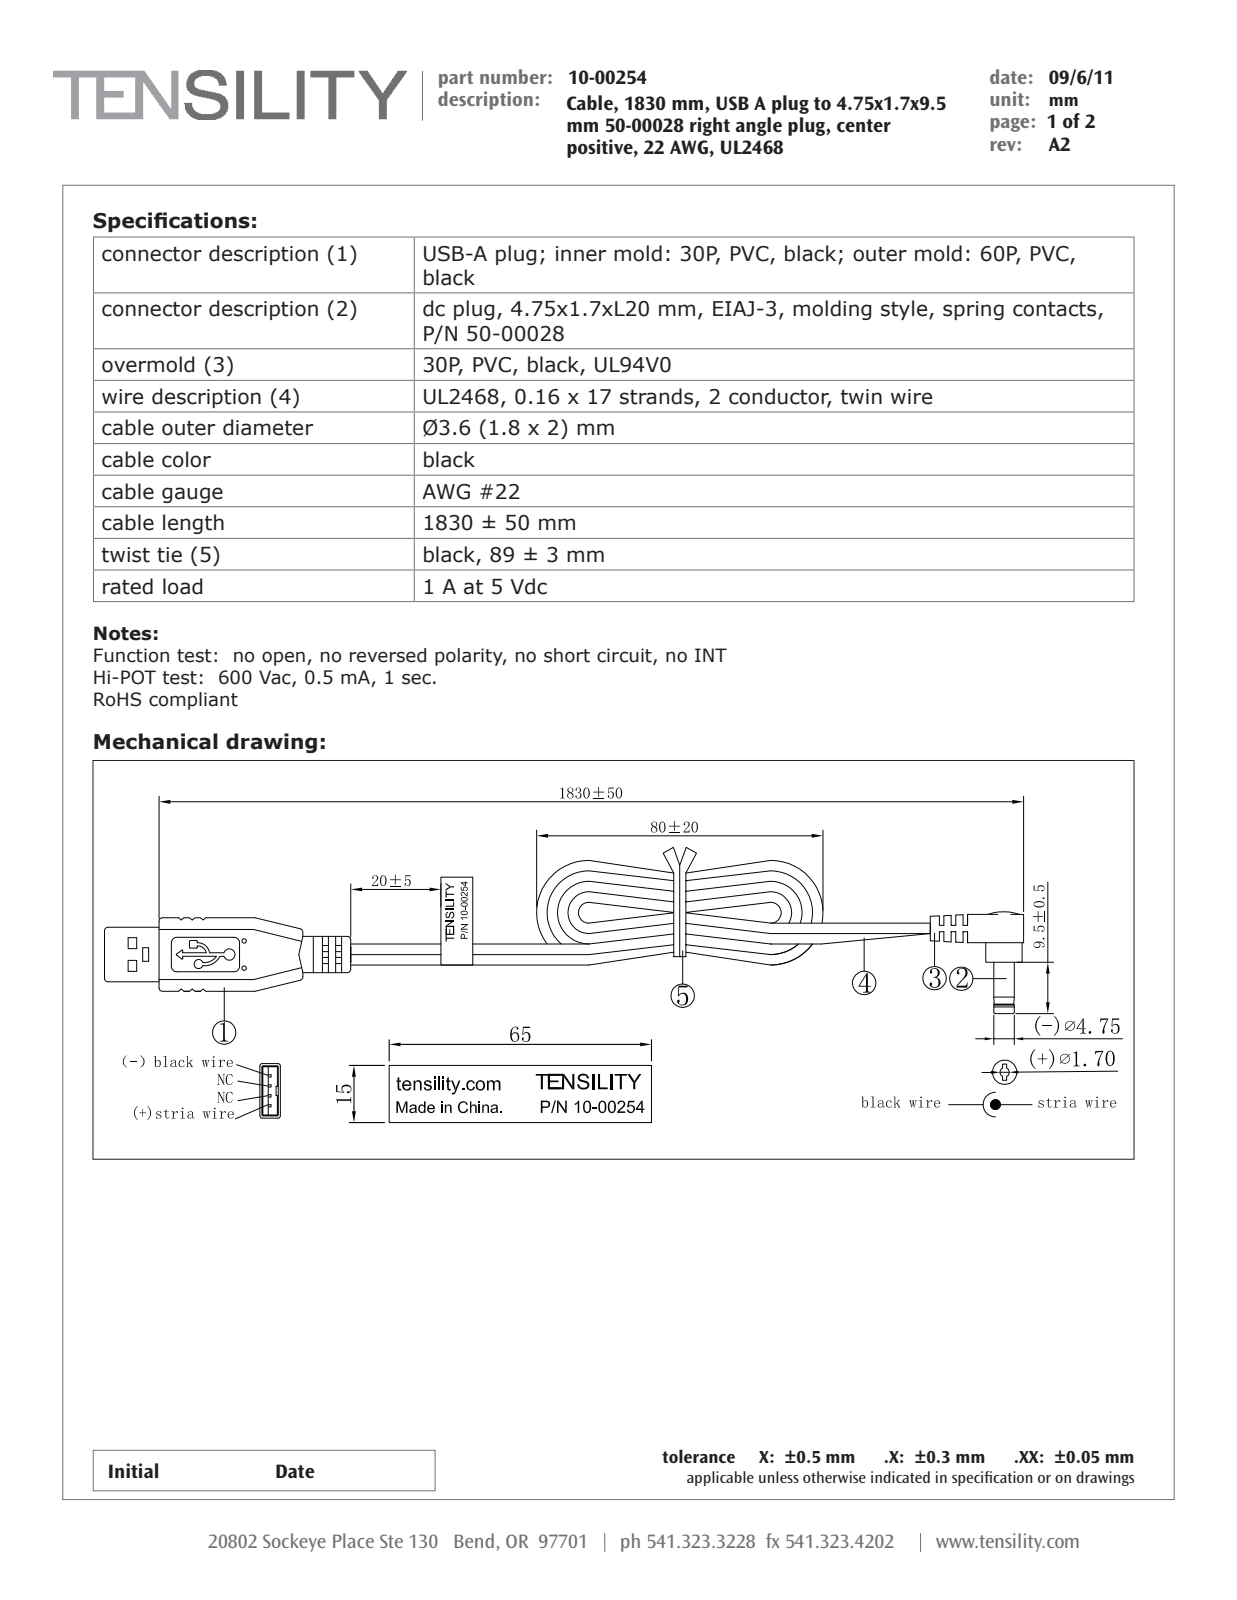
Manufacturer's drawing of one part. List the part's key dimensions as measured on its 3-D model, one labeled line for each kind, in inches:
Part name (STEP PRODUCT): 24-00062_default; 24-00023; 50-00028; Label 254 (+8 more)
STEP written by: SolidWorks 2015 (CONFIG_CONTROL_DESIGN)
Units: inches
Bodies: 59 solids, 1191 faces (600 planar, 314 cylindrical, 277 other)
Overall size (bounding box): 8.244 × 1.86 × 0.339
Volume: 0.453 in³ · Surface area: 20.33 in²
Round holes (diameter × count): ⌀0.033 ×2, ⌀0.047 ×1, ⌀0.165 ×1, ⌀0.187 ×1
Round bosses / shafts (diameter × count): ⌀0.075 ×2, ⌀0.315 ×1, ⌀0.286 ×1, ⌀0.213 ×1, ⌀0.19 ×1, ⌀0.189 ×1, ⌀0.185 ×1, ⌀0.174 ×1
Partial cylindrical surfaces — rounded edges, fillets, slot ends (radius × count): R0.004 ×49, R0.008 ×12, R0.012 ×12, R0.02 ×12, R0.006 ×9, R0.01 ×8, R0.03 ×8, R0.016 ×4
Main face-to-face distances: 0.077, 0.073, 0.071, 0.079, 0.152, 0.254, 0.092, 0.081, 0.177, 0.089
Hole centre spacings: 0.07
